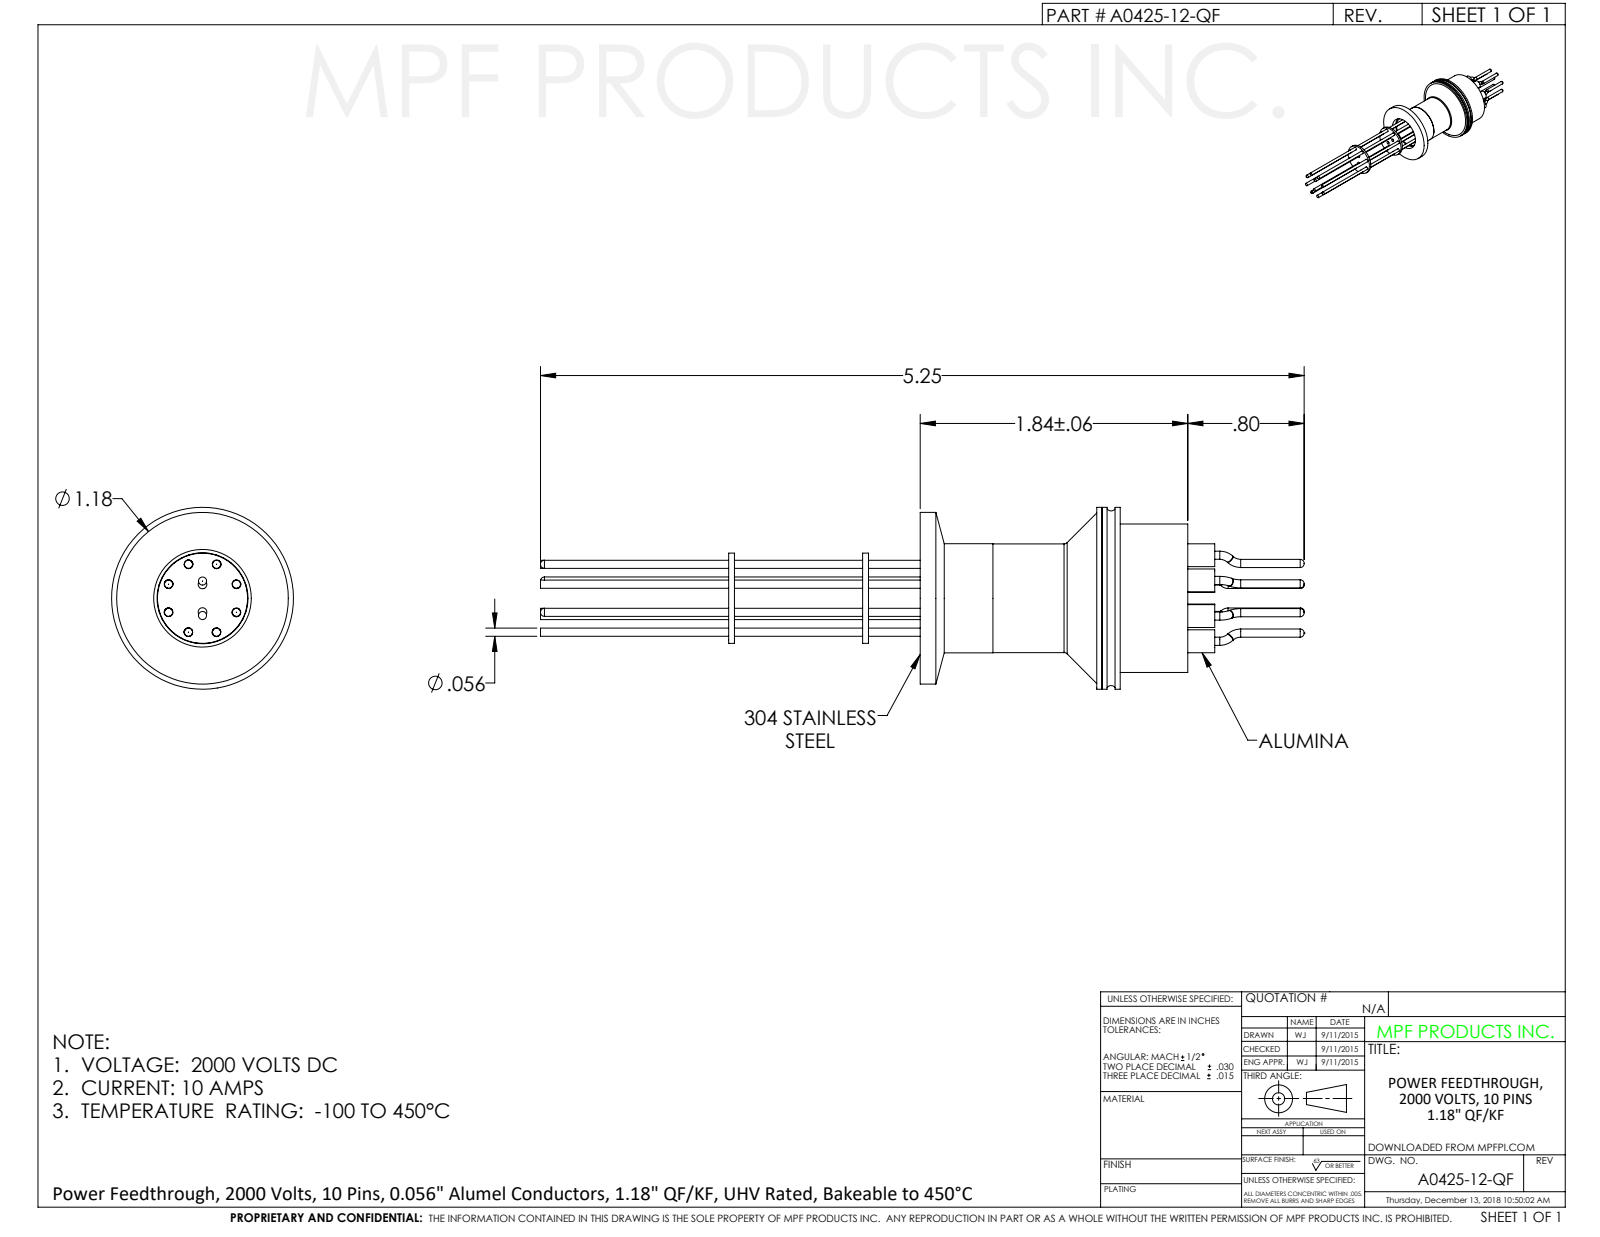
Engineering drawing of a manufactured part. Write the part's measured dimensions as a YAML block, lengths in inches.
part_name: "A0425-12-QF"
step_written_by: "SolidWorks 2012 (CONFIG_CONTROL_DESIGN)"
units: inches
bodies: {solids: 1, faces: 449, planar: 63, cylindrical: 232, other: 154}
overall_size: [5.25, 1.25, 1.25]
volume: 0.647
surface_area: 27.21
round_holes:
  - {diameter: 0.159, count: 10}
  - {diameter: 0.625, count: 1}
  - {diameter: 0.675, count: 1}
  - {diameter: 0.683, count: 1}
  - {diameter: 0.94, count: 1}
  - {diameter: 0.96, count: 1}
  - {diameter: 0.97, count: 1}
round_bosses_or_shafts:
  - {diameter: 0.056, count: 30}
  - {diameter: 0.187, count: 10}
  - {diameter: 0.171, count: 10}
  - {diameter: 1.25, count: 1}
  - {diameter: 1.18, count: 1}
  - {diameter: 1.02, count: 1}
  - {diameter: 0.957, count: 1}
  - {diameter: 0.75, count: 1}
face_to_face_distances: [0.04, 0.641, 1.805, 1.755, 0.05, 0.43, 1.375, 0.38, 0.125, 0.555]
hole_center_spacings: [0.13, 0.245, 0.269, 0.38, 0.452, 0.473, 0.474, 0.51]
